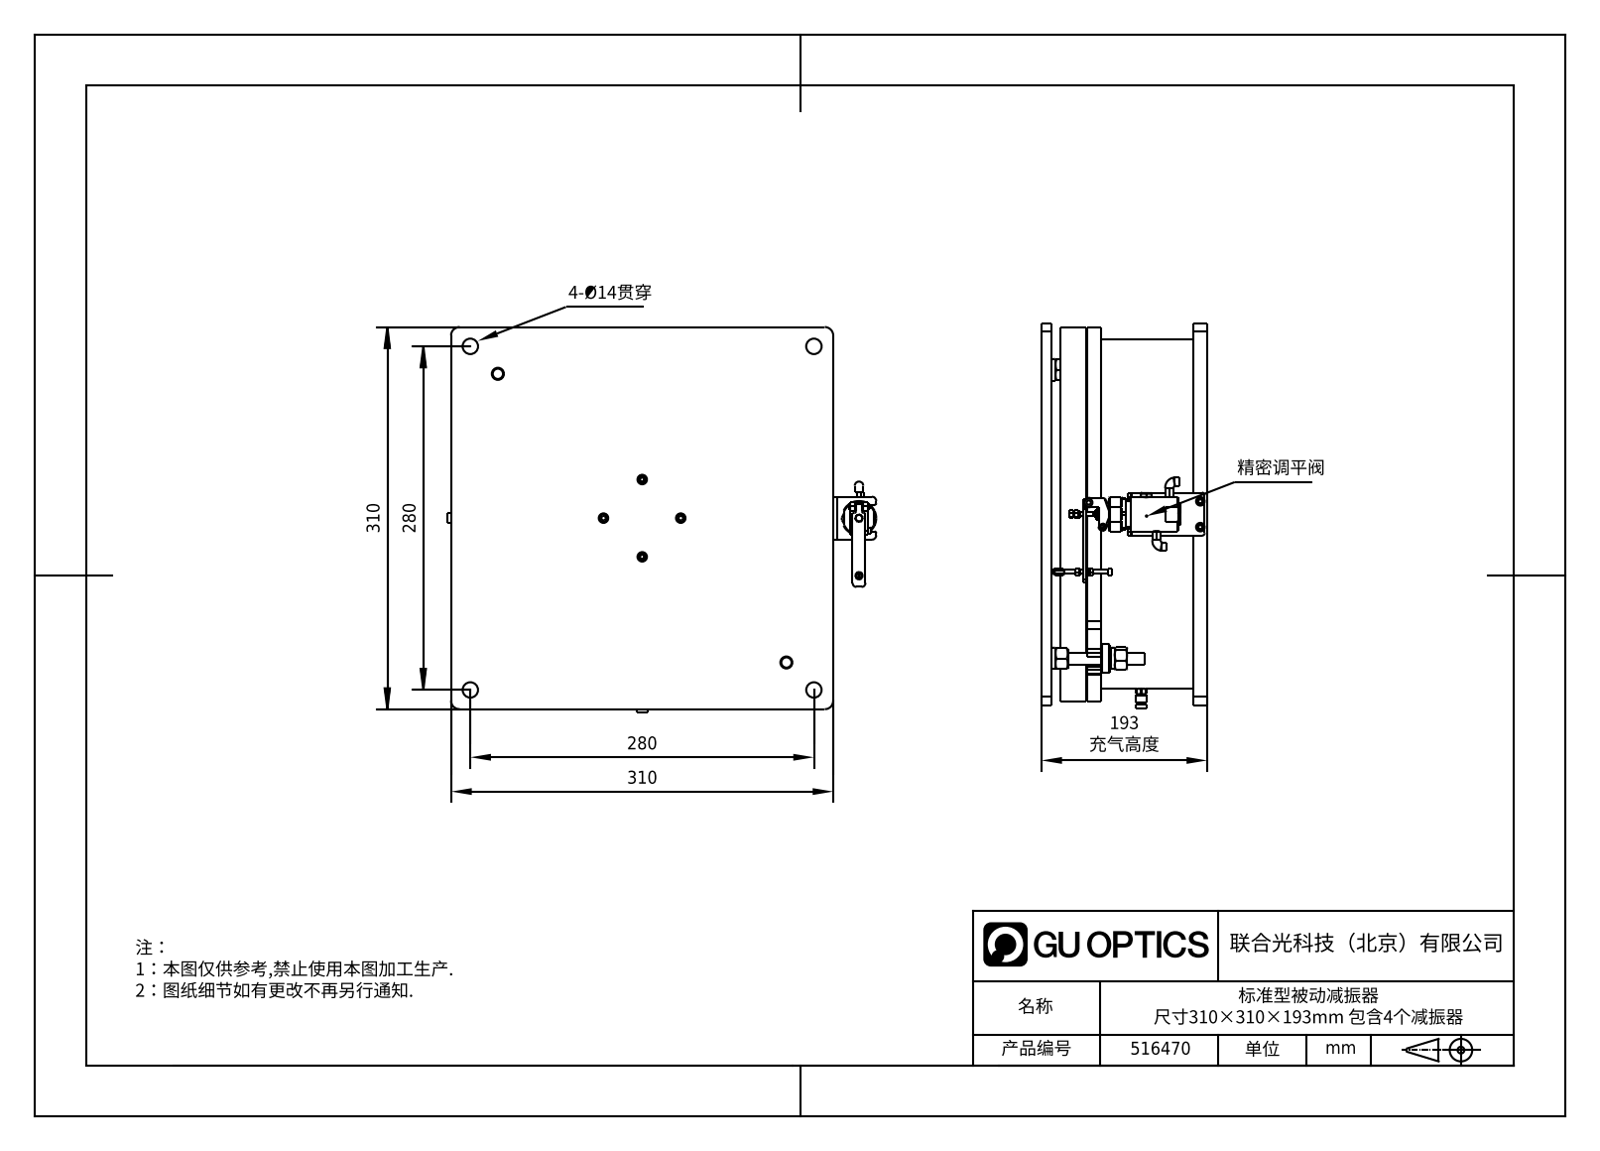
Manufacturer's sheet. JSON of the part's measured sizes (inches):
{"part_name": "516470", "step_written_by": "SolidWorks 2020 (CONFIG_CONTROL_DESIGN)", "units": "inches", "bodies": {"solids": 0, "faces": 463, "planar": 263, "cylindrical": 141, "other": 59}, "overall_size": [14.252, 12.283, 7.598], "round_holes": [[0.551, 4], [0.382, 3], [0.5, 3], [0.197, 1], [0.453, 1], [0.512, 1], [12.205, 1]], "round_bosses_or_shafts": [[0.472, 5], [0.433, 5], [0.394, 4], [1.181, 3], [0.496, 3], [0.409, 3], [0.333, 3], [0.319, 3]], "partial_cylinders_radius": [[0.197, 10], [0.394, 10], [0.012, 3], [0.079, 3], [0.276, 3], [0.118, 2], [0.177, 2], [0.029, 1]], "face_to_face_distances": [0.472, 7.126, 6.654, 7.598, 1.89, 5.236, 4.764, 2.362, 1.417, 0.394], "hole_center_spacings": [7.795, 11.024, 1.614, 5.728, 5.789, 5.952, 13.932, 15.59]}
